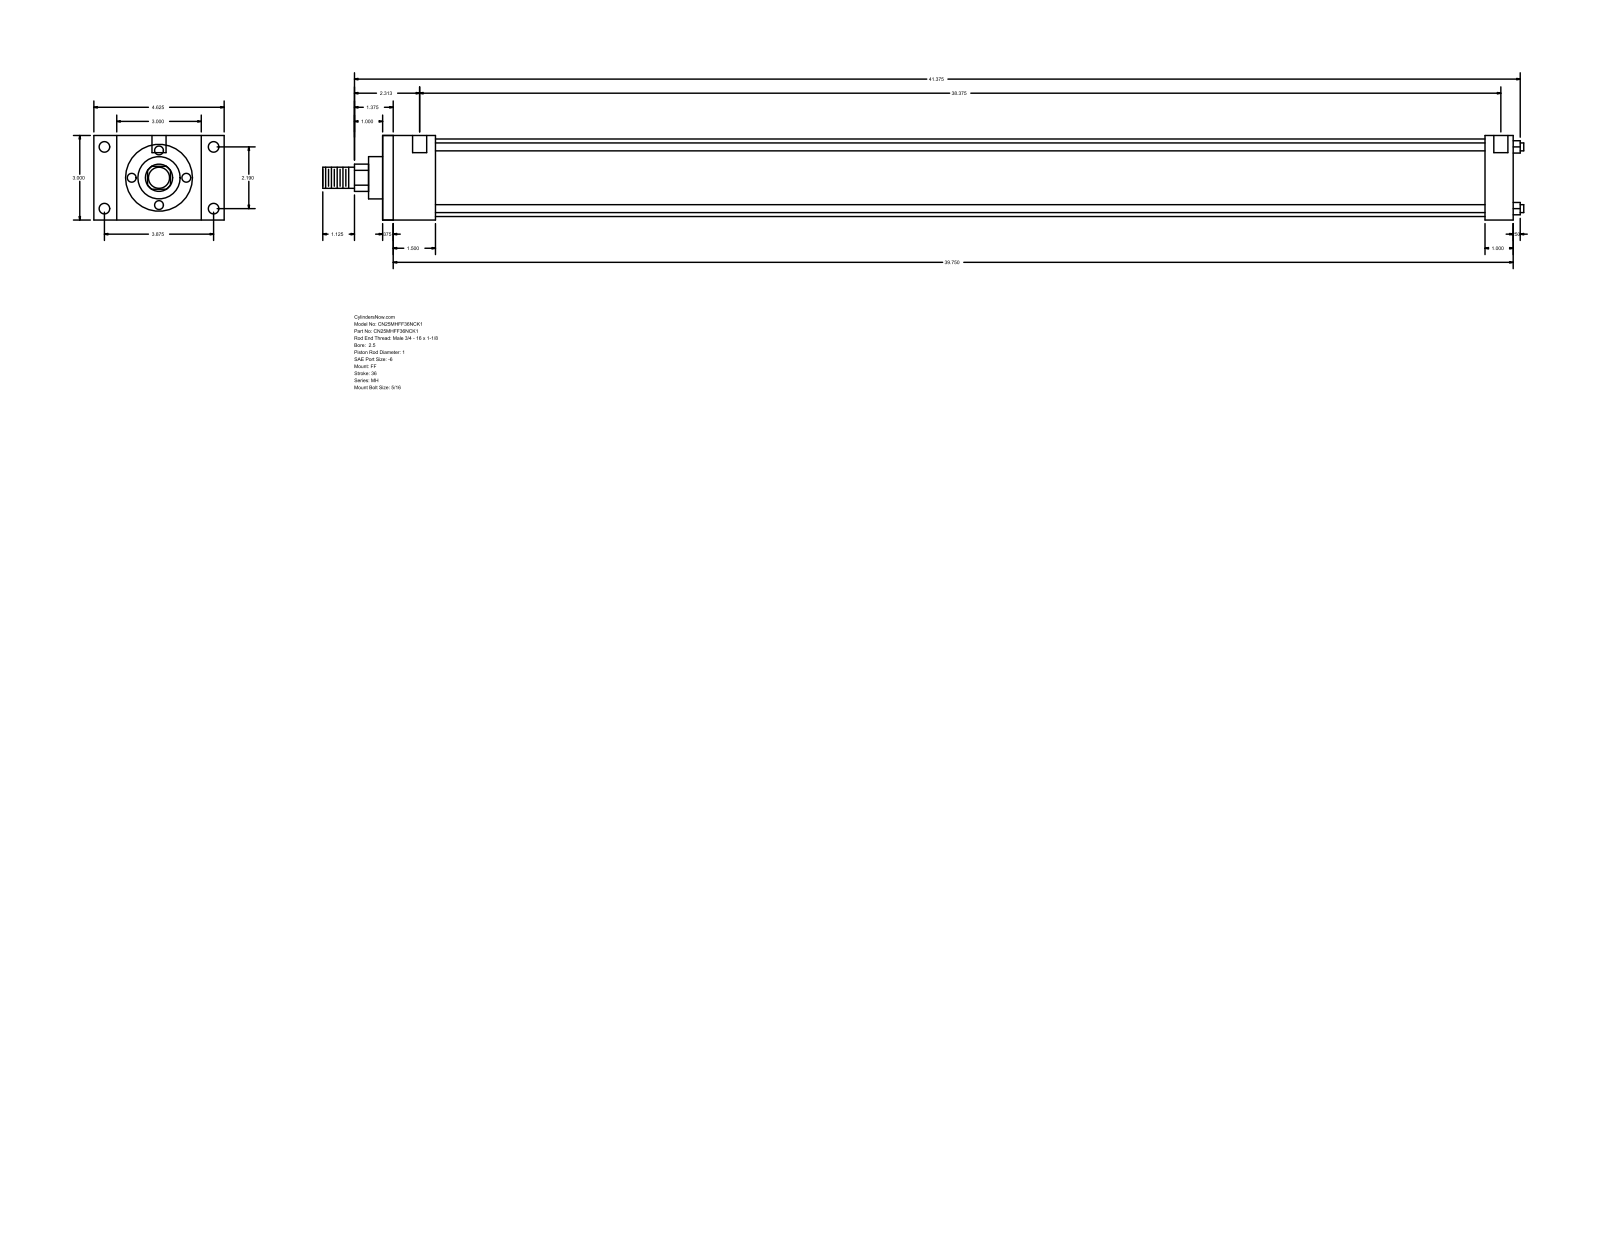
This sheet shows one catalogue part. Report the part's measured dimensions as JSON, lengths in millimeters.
{"part_name": "MH_FF__0250_1", "step_written_by": "GSSL Pune (CONFIG_CONTROL_DESIGN)", "units": "millimeters", "bodies": {"solids": 0, "faces": 92, "planar": 64, "cylindrical": 28, "other": 0}, "overall_size": [1082.67, 117.47, 76.2], "round_holes": [[5.56, 4], [9.53, 4], [12.7, 2]], "round_bosses_or_shafts": [[7.14, 4], [69.85, 1], [38.1, 1], [25.4, 1], [19.05, 1]], "partial_cylinders_radius": [[12.29, 1]], "face_to_face_distances": [76.2, 1019.18, 9.52, 1009.66, 47.63, 993.77, 38.11, 984.25, 946.14, 971.55], "hole_center_spacings": [55.62, 98.42, 113.05, 982.66, 3.18, 4.76, 974.72, 977.9]}
